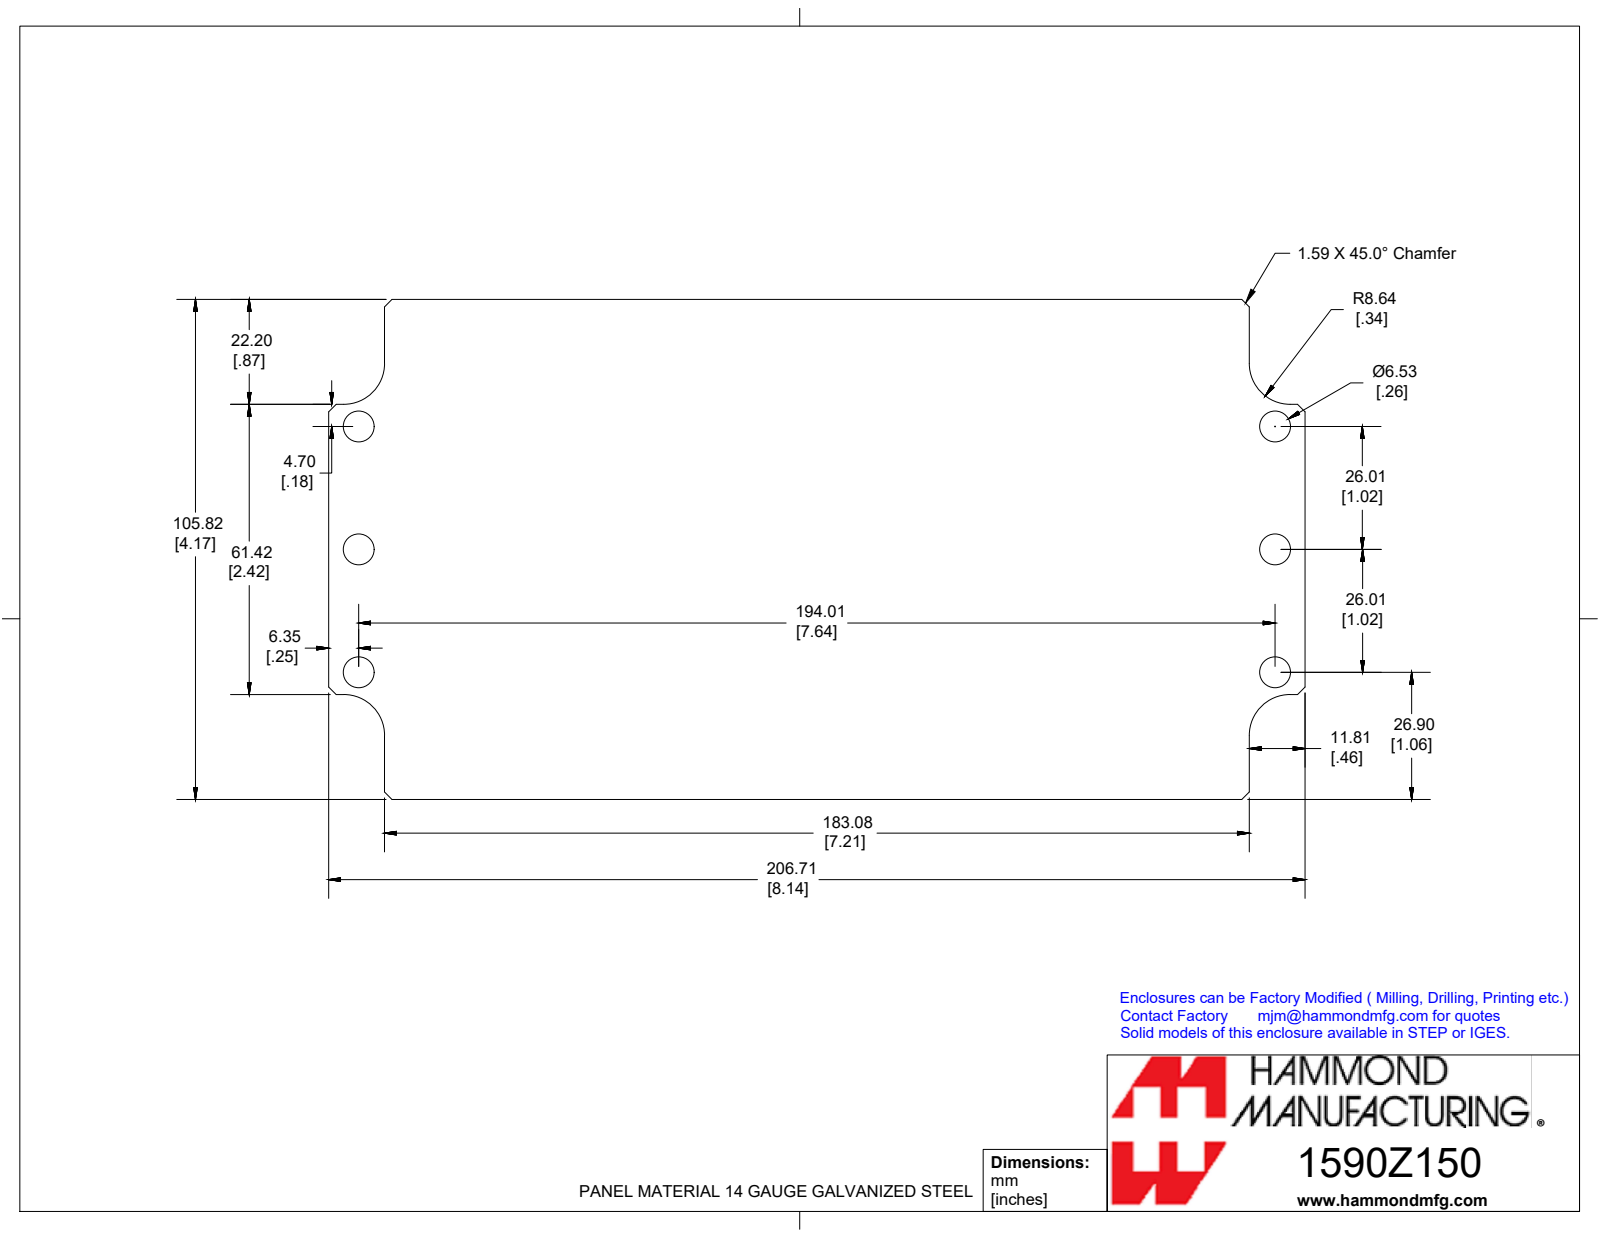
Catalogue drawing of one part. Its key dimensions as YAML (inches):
part_name: "1590Z150PL"
step_written_by: "SolidWorks 2019 (CONFIG_CONTROL_DESIGN)"
units: inches
bodies: {solids: 1, faces: 32, planar: 22, cylindrical: 10, other: 0}
overall_size: [8.138, 4.166, 0.064]
volume: 2.035
surface_area: 65.91
round_holes:
  - {diameter: 0.257, count: 6}
partial_cylinders:
  - {radius: 0.34, count: 4}
face_to_face_distances: [0.063, 4.166, 8.138, 0.465, 7.673, 7.208, 0.289, 7.664, 0.874, 3.292]
hole_center_spacings: [1.024, 7.706, 7.638, 2.048, 7.907]
